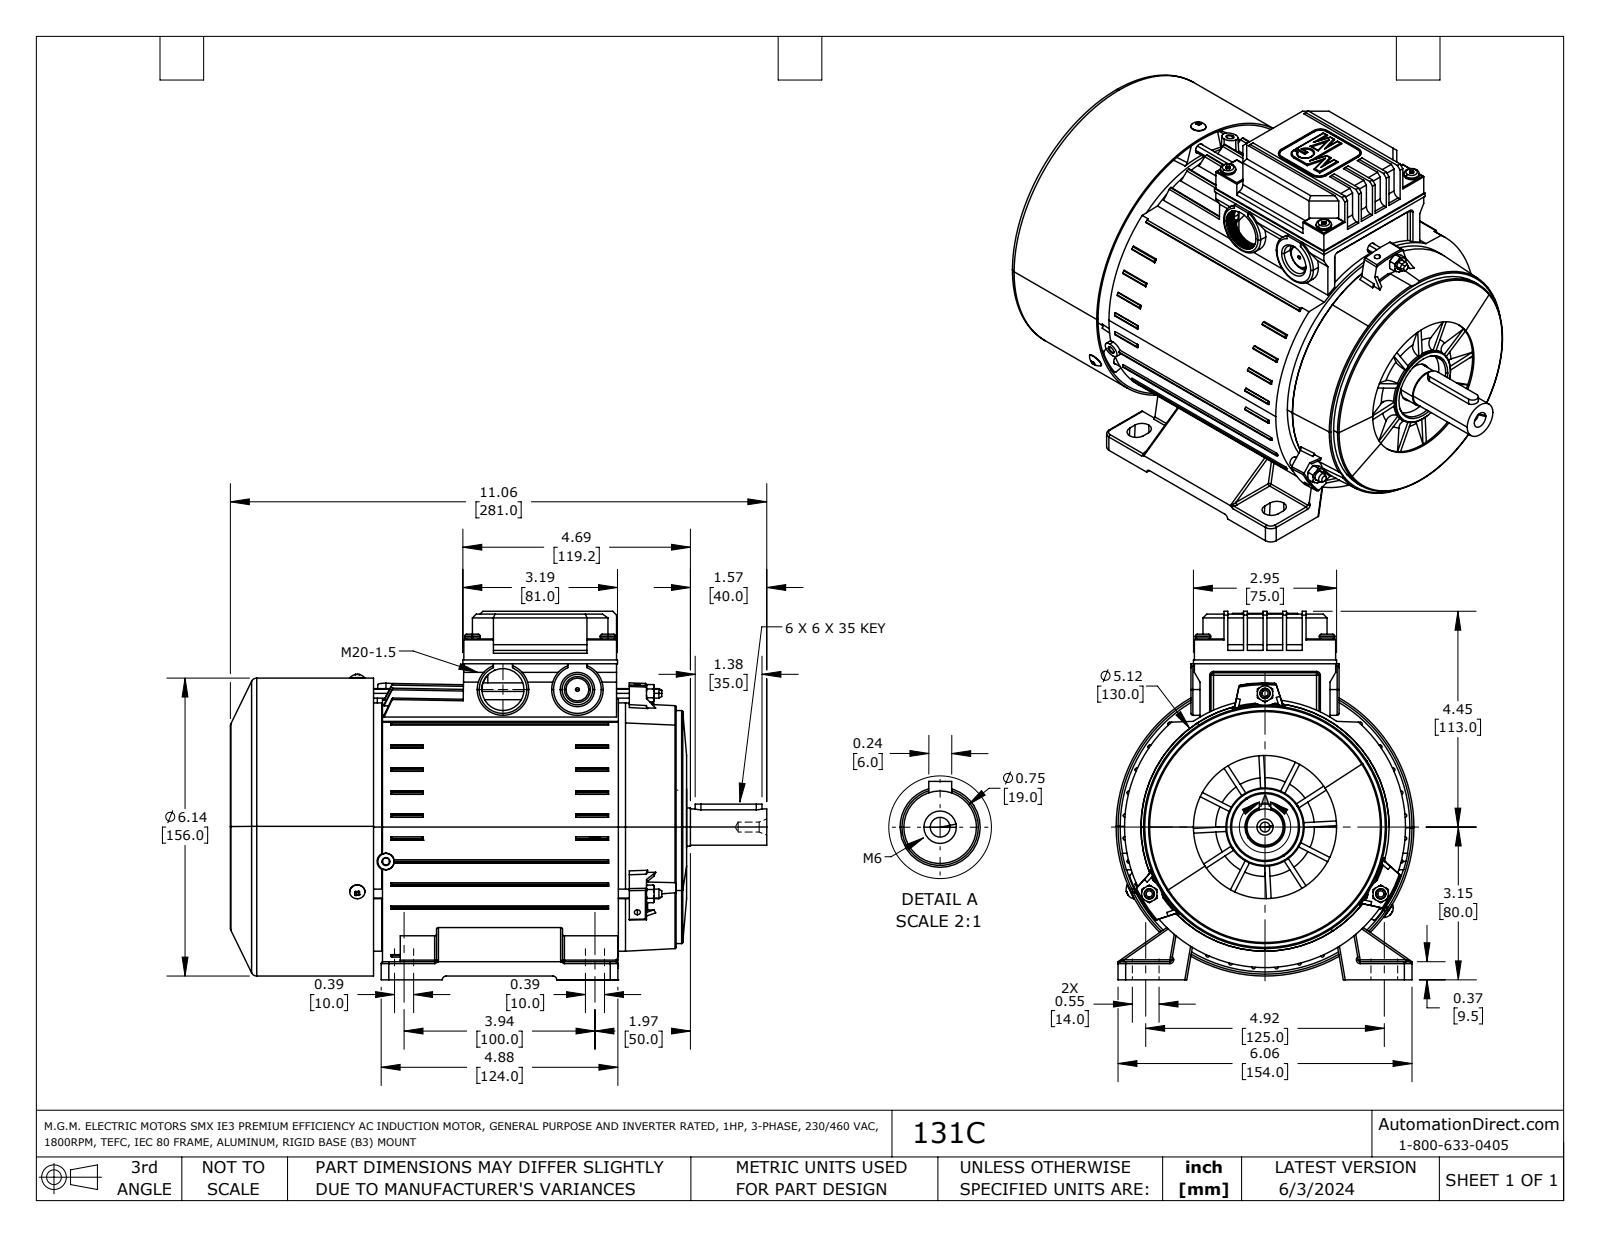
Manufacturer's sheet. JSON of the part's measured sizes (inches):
{"part_name": "131C", "step_written_by": "SolidWorks 2021 (AUTOMOTIVE_DESIGN)", "units": "inches", "bodies": {"solids": 19, "faces": 3233, "planar": 1132, "cylindrical": 1153, "other": 948}, "overall_size": [11.063, 7.598, 6.142], "volume_in3": 72.06, "surface_area_in2": 730, "round_holes": [[0.118, 12], [0.146, 8], [0.217, 7], [0.126, 6], [0.157, 4], [0.177, 3], [0.276, 3], [0.205, 1], [0.315, 1], [0.63, 1], [0.827, 1], [0.846, 1]], "round_bosses_or_shafts": [[0.118, 10], [0.315, 7], [0.138, 4], [1.063, 3], [0.197, 3], [0.079, 3], [6.142, 1], [5.119, 1]], "partial_cylinders_radius": [[0.039, 298], [0.035, 48], [0.016, 36], [0.008, 32], [0.02, 30], [0.035, 28], [0.004, 16], [0.033, 16]], "face_to_face_distances": [0.079, 0.945, 0.2, 0.098, 6.142, 0.138, 0.039, 8.031, 7.831, 8.071], "hole_center_spacings": [0.478, 0.571, 0.748, 1.102, 1.22, 1.222, 1.559, 1.576]}
